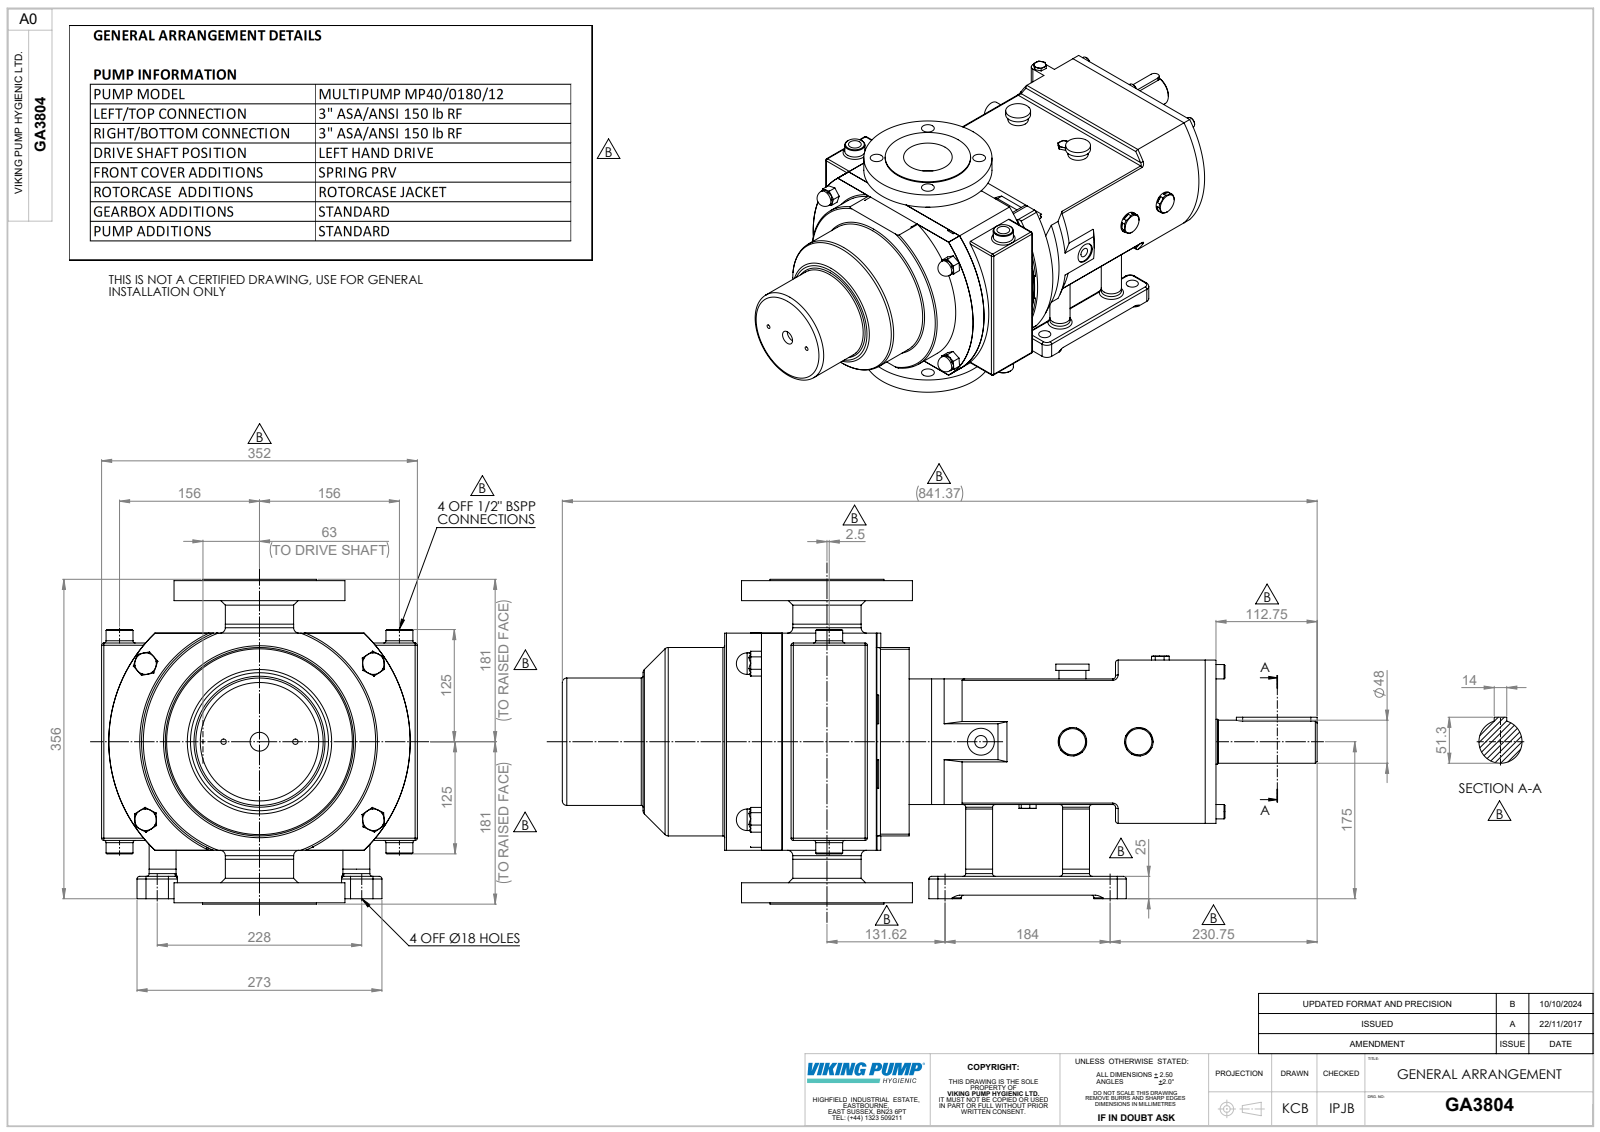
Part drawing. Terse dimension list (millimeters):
name: Copy of CP-MP40S Jacket Rotorcase^GA3804; GA3804; Copy of Z94-5301-55 - 3 INCH ASA 150^GA3804; Copy of CP-MP40 Spring PRV^GA3804 (+1 more)
written by: SolidWorks 2023 (AUTOMOTIVE_DESIGN)
unit: mm
bodies: 6 solids, 1080 faces (395 planar, 345 cylindrical, 340 other)
size: 841.37 × 362 × 352
volume: 36 550 000 mm³; area: 1 469 000 mm²
holes: 6× ⌀19, 4× ⌀18, 3× ⌀10.2, 2× ⌀6, 2× ⌀11.89, 2× ⌀18.97, 2× ⌀35, 1× ⌀13.83, 1× ⌀21, 1× ⌀30, 1× ⌀72.3
bosses: 12× ⌀30, 8× ⌀24, 6× ⌀16, 2× ⌀110, 2× ⌀70, 2× ⌀37, 2× ⌀31.75, 1× ⌀250
rounds: 24× R10, 22× R3, 20× R8, 12× R2.5, 10× R6, 4× R5, 4× R11, 2× R7
face distances: 23, 51, 191, 21, 30, 212, 161, 140, 483.62, 506.62
hole spacings: 76.2, 107.76, 152.4, 172.14, 250.19, 20.73, 40, 54.04
